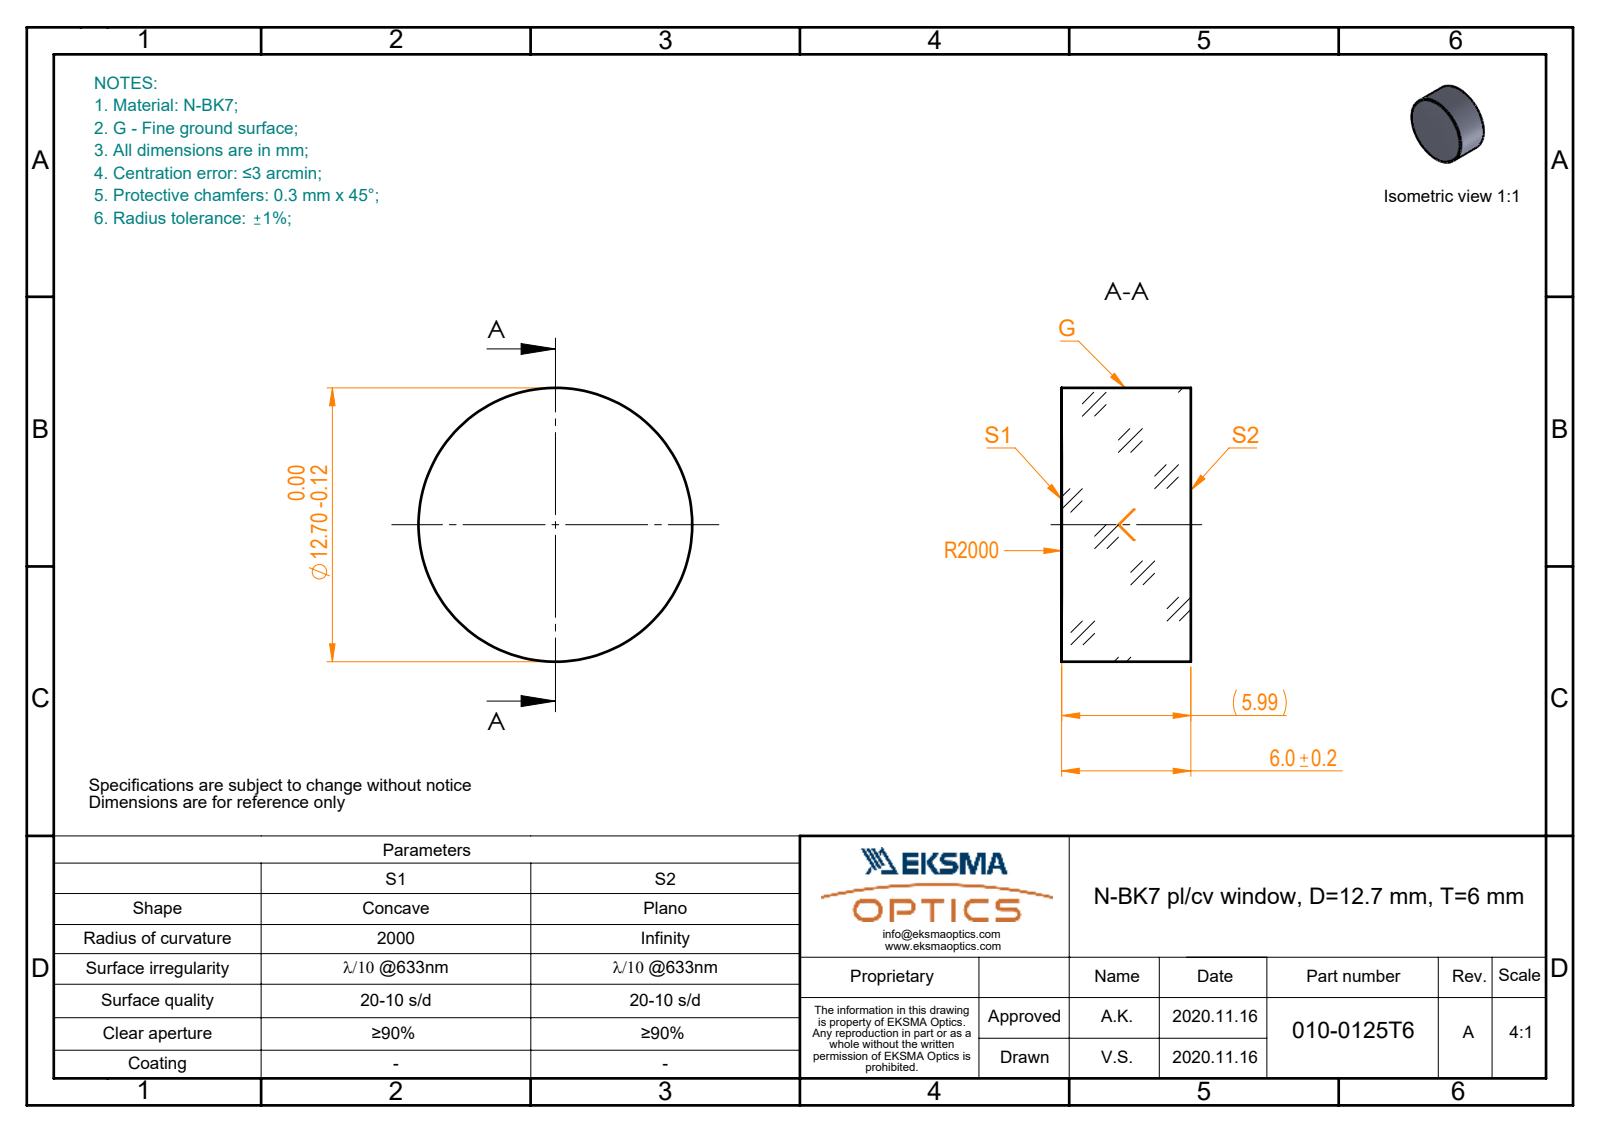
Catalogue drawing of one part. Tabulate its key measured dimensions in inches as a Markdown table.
| quantity | value |
| --- | --- |
| part name | 010-0125T6_N-BK7_PCV_window |
| STEP written by | SolidWorks 2019 (CONFIG_CONTROL_DESIGN) |
| units | inches |
| bodies | 1 solid, 5 faces (1 planar, 2 cylindrical, 2 other) |
| overall size | 0.5 × 0.5 × 0.236 |
| volume | 0.046 in³ |
| surface area | 0.764 in² |
| round bosses / shafts (diameter × count) | 0.5 × 1 |
